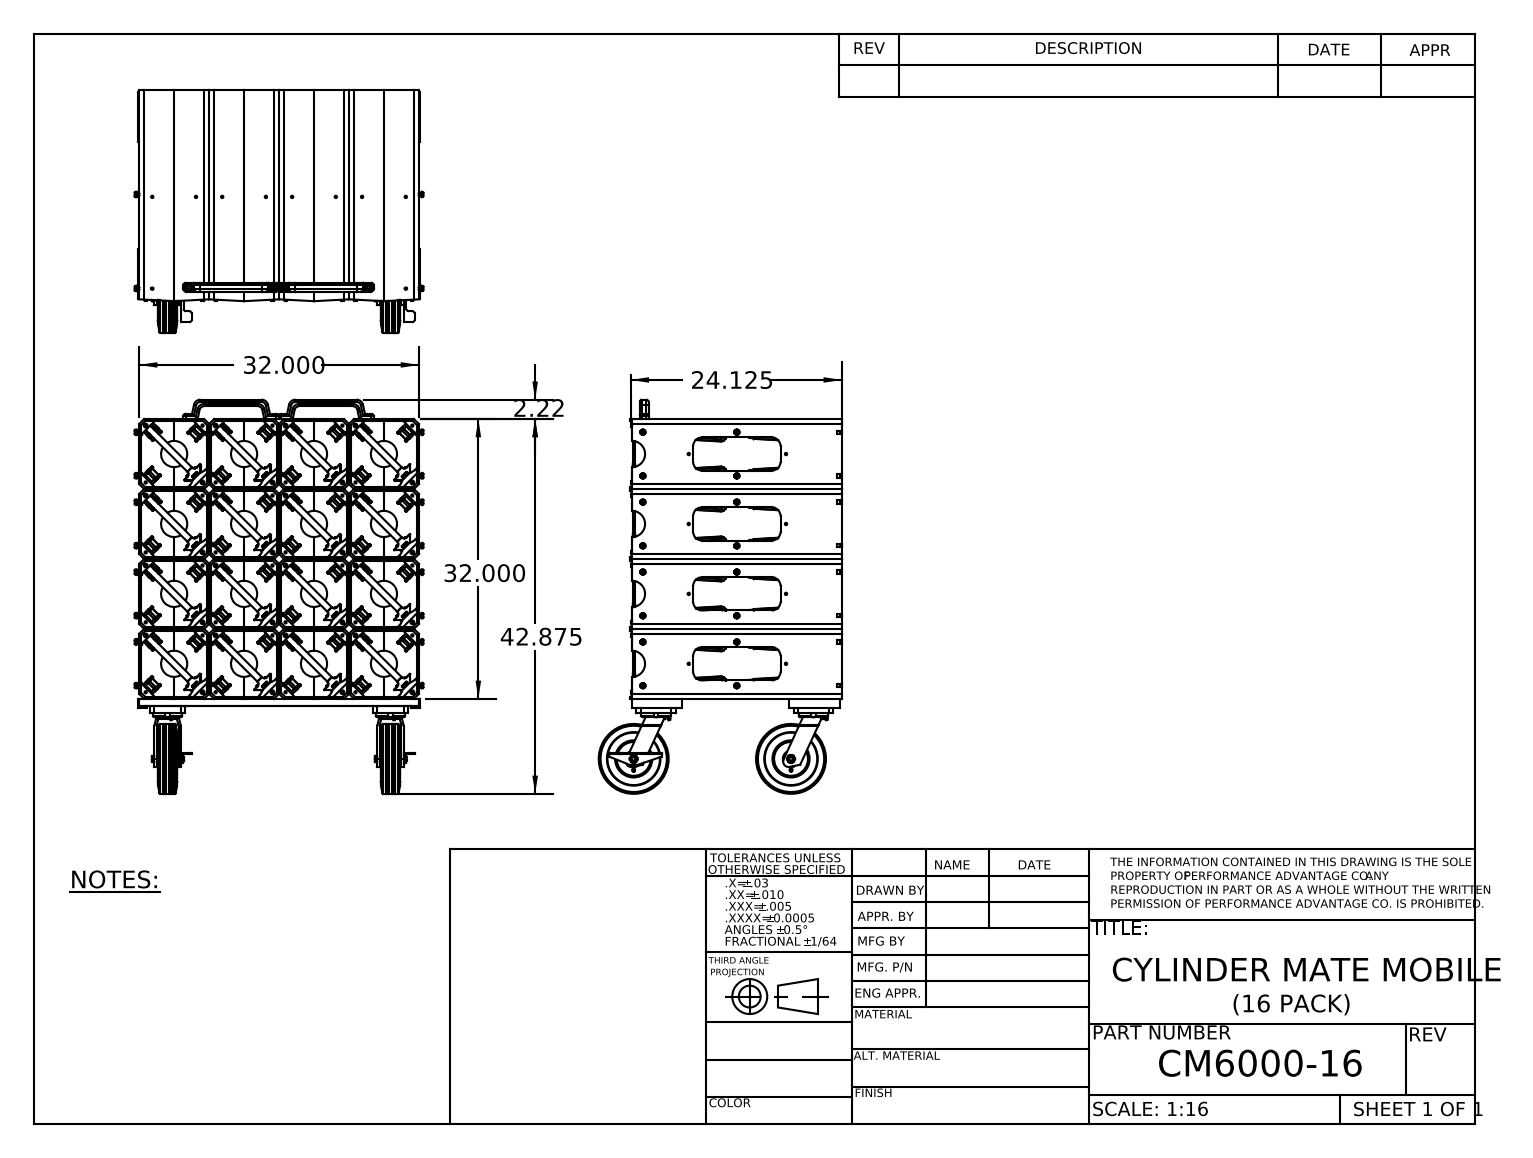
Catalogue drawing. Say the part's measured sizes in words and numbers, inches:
The part is named "CM6000-16; 7020x24(cmate mobile)_32; A416S x 5.750_SHORT; 9SF8X3-SB (+8 more)". Its 3-D file was written by "SolidWorks 2010 (CONFIG_CONTROL_DESIGN)". It is 584 solids with 28148 faces: 9904 planar, 7528 cylindrical and 10716 other. Overall it measures 45.093 by 33 by 27.803 inches. Its volume is 4 700 cubic inches and its surface area 31 637 square inches. Round holes: 64 of diameter 0.26, 60 of diameter 0.266, 16 of diameter 0.201, 4 of diameter 0.343, 4 of diameter 0.733, 3 of diameter 0.5, 3 of diameter 0.625, 3 of diameter 0.687, 3 of diameter 0.75, 3 of diameter 1.126, 3 of diameter 1.188, 3 of diameter 4. Round bosses or shafts: 32 of diameter 0.437, 32 of diameter 0.25, 16 of diameter 3, 16 of diameter 0.585, 4 of diameter 3.4, 4 of diameter 2.1, 4 of diameter 1, 4 of diameter 0.312. Partial cylindrical surfaces (rounded edges, fillets, slot ends): 1548 of radius 0.094, 1232 of radius 0.016, 271 of radius 0.031, 256 of radius 0.296, 256 of radius 0.452, 170 of radius 0.062, 144 of radius 0.125, 128 of radius 0.1. The main face-to-face distances are 8, 0.25, 16, 7.75, 8.25, 15.75, 24, 23.75, 7.5, 16.25. The hole center spacings are 8, 6.5, 16, 10.308, 24, 25.298, 5, 9.193.
